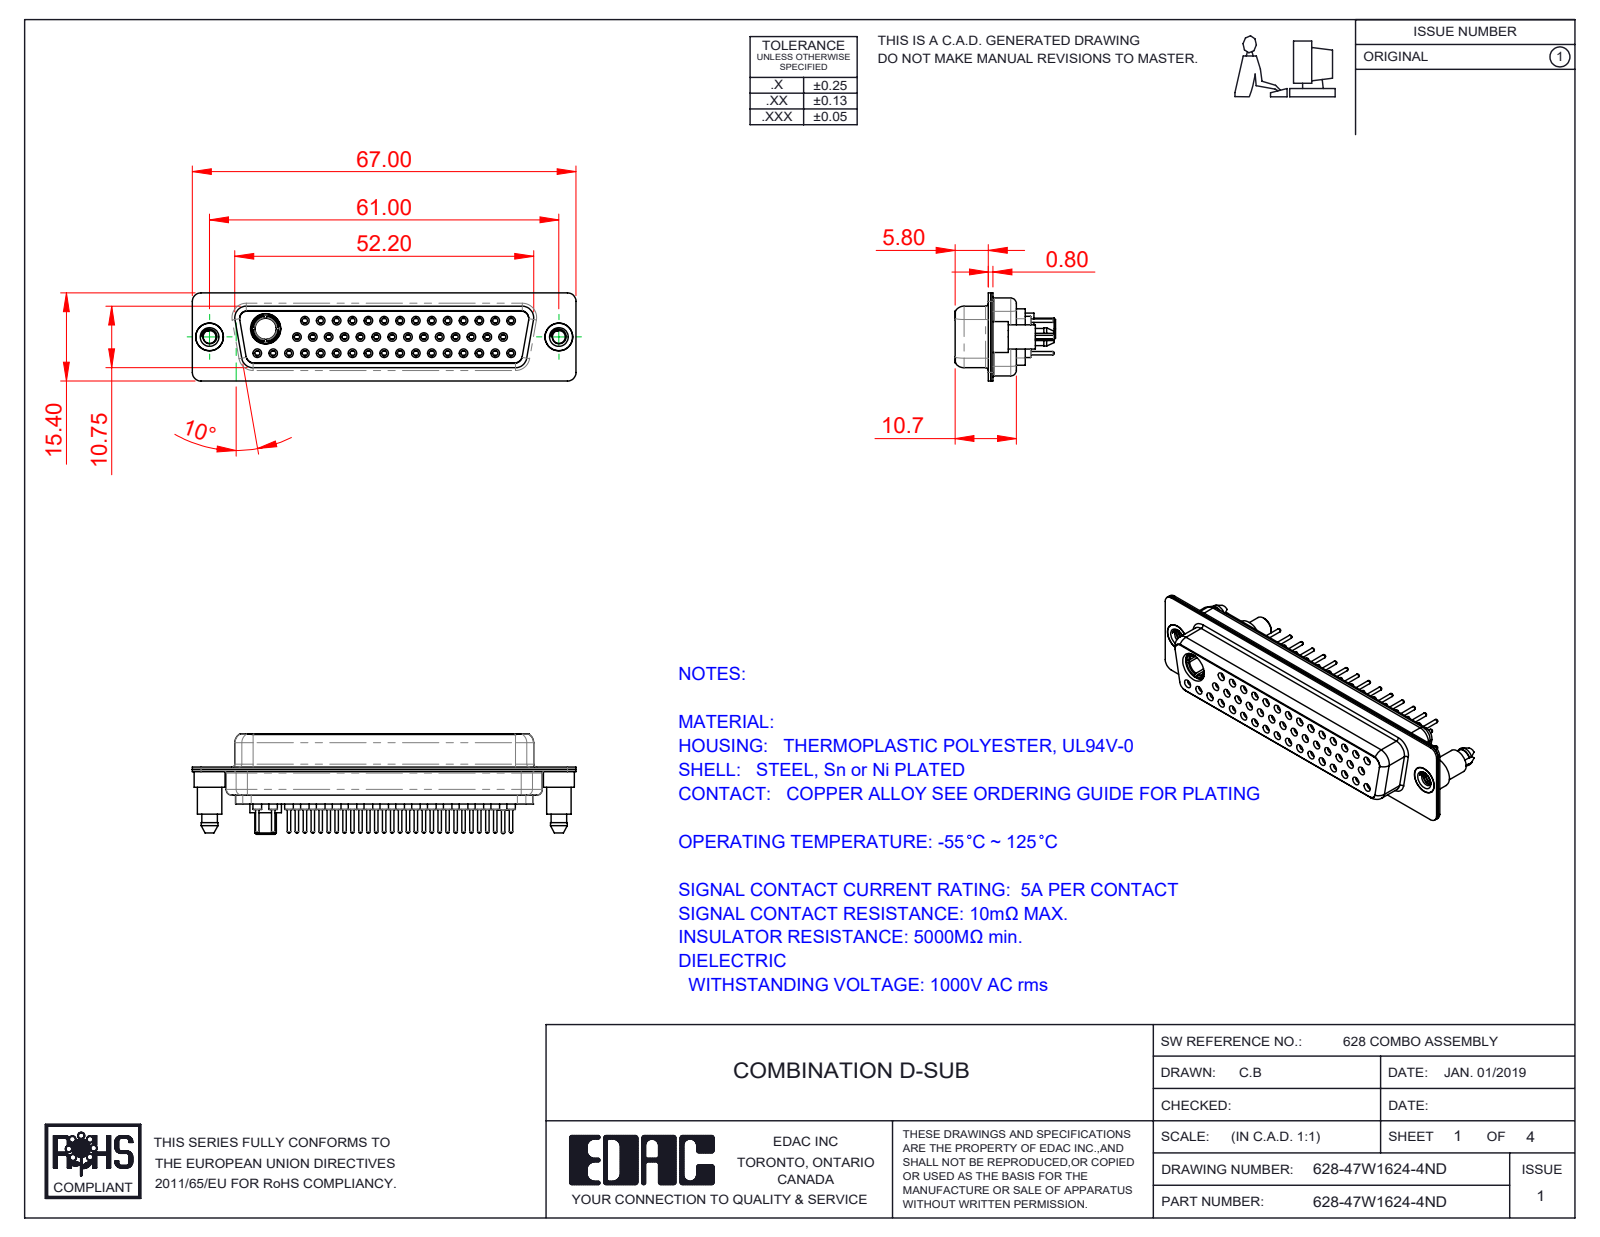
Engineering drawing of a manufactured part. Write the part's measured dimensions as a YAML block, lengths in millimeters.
part_name: "628Combo Shell Rear_50 Contacts; 628Combo Contact Row 1_24; 628Combo Threaded Boardlock_D; 628Combo Contact Row 2_24 (+5 more)"
step_written_by: "SolidWorks 2016 (CONFIG_CONTROL_DESIGN)"
units: millimeters
bodies: {solids: 53, faces: 2937, planar: 799, cylindrical: 1074, other: 1064}
overall_size: [67, 17.55, 15.4]
volume: 7240
surface_area: 15040
round_holes:
  - {diameter: 1.1, count: 46}
  - {diameter: 0.9, count: 45}
  - {diameter: 1.5, count: 45}
  - {diameter: 2, count: 45}
  - {diameter: 1.6, count: 31}
  - {diameter: 1.7, count: 14}
  - {diameter: 4.85, count: 3}
  - {diameter: 2.26, count: 2}
  - {diameter: 4, count: 2}
  - {diameter: 4.05, count: 2}
  - {diameter: 3.7, count: 1}
  - {diameter: 5.3, count: 1}
round_bosses_or_shafts:
  - {diameter: 2.2, count: 46}
  - {diameter: 0.6, count: 46}
  - {diameter: 1.6, count: 15}
  - {diameter: 5.4, count: 2}
  - {diameter: 4.95, count: 2}
  - {diameter: 4.8, count: 2}
  - {diameter: 4.25, count: 2}
  - {diameter: 5.5, count: 1}
partial_cylinders:
  - {radius: 1.5, count: 18}
  - {radius: 1.35, count: 12}
  - {radius: 2, count: 12}
  - {radius: 1.6, count: 10}
  - {radius: 0.25, count: 4}
  - {radius: 0.5, count: 4}
  - {radius: 0.6, count: 4}
  - {radius: 0.65, count: 4}
face_to_face_distances: [0.4, 11.33, 6.45, 6.05, 1.87, 12.25, 6.2, 5.8, 10.35, 10.93]
hole_center_spacings: [3.16, 2.77, 5.54, 8.31, 11.08, 13.85, 16.62, 19.39]
